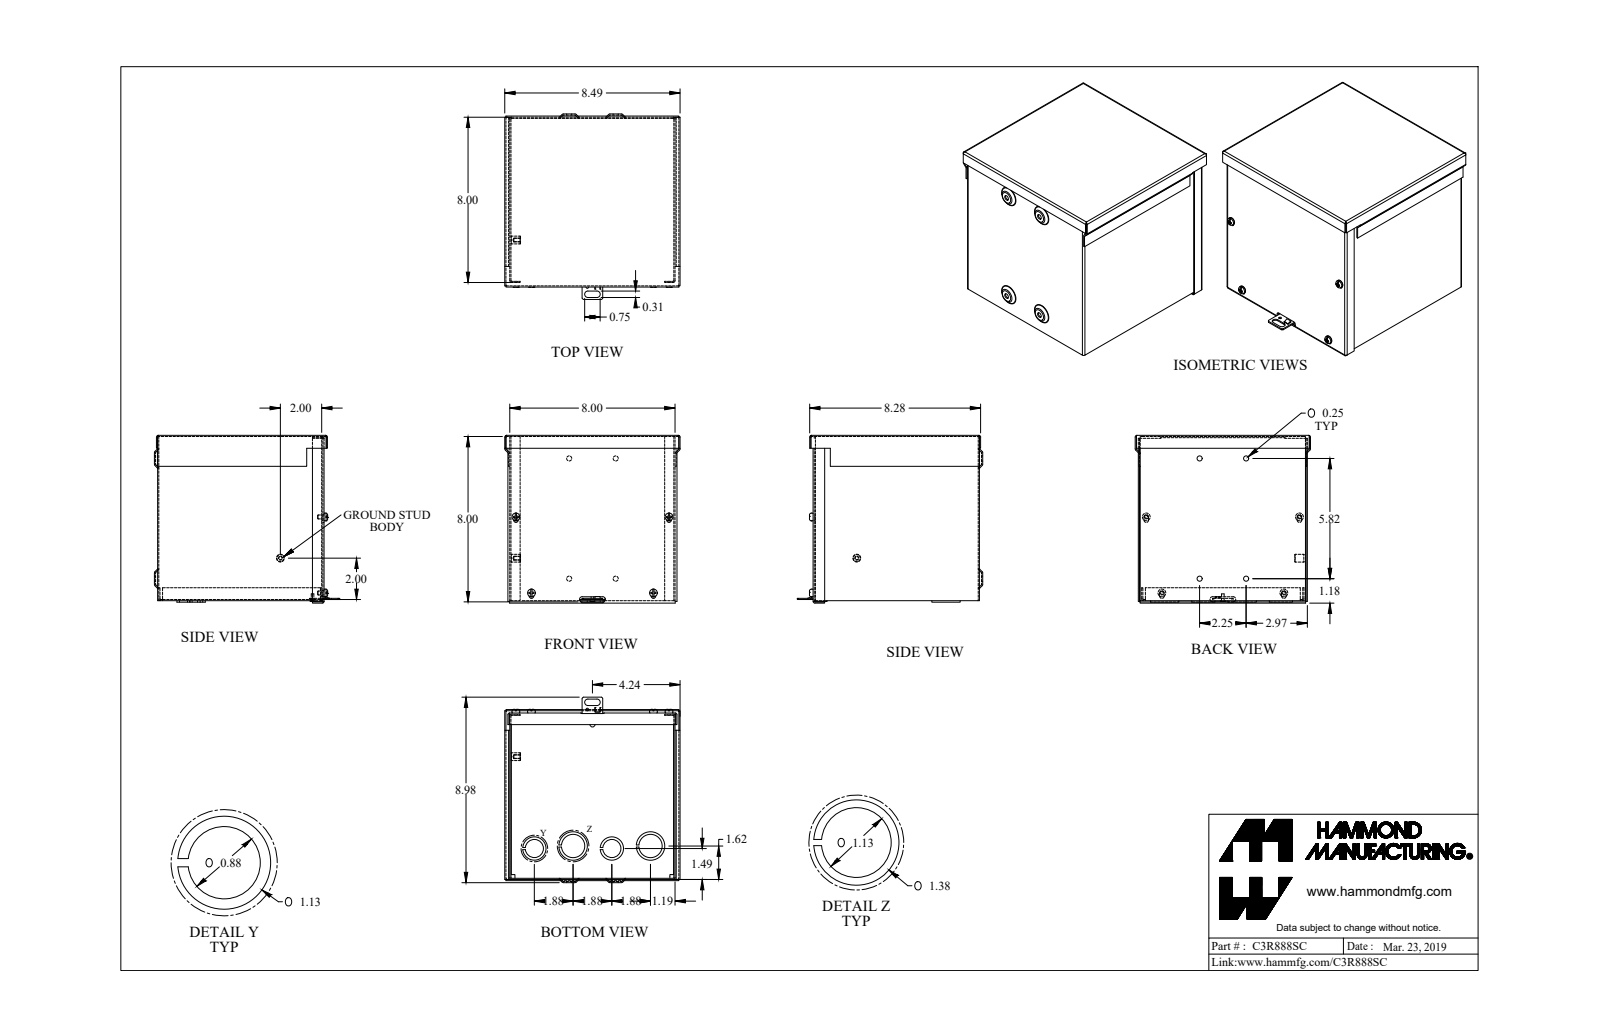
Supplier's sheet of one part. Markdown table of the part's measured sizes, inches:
| quantity | value |
| --- | --- |
| part name | C3R888SC_Default |
| STEP written by | SolidWorks 2019 (CONFIG_CONTROL_DESIGN) |
| units | inches |
| bodies | 11 solids, 424 faces (223 planar, 115 cylindrical, 86 other) |
| overall size | 8.977 × 8.489 × 8.12 |
| volume | 26.25 in³ |
| surface area | 929 in² |
| round holes (diameter × count) | 0.17 × 4, 0.25 × 4, 1.125 × 2, 0.125 × 1, 0.137 × 1, 0.156 × 1, 0.875 × 1, 0.875 × 1 |
| round bosses / shafts (diameter × count) | 0.375 × 4, 0.19 × 4, 1.375 × 2, 1.125 × 2, 0.375 × 1, 0.125 × 1 |
| partial cylindrical surfaces (radius × count) | 0.029 × 21, 0.086 × 21, 0.109 × 8, 0.125 × 8, 0.156 × 2 |
| main face-to-face distances | 0.057, 8, 7.943, 0.057, 7.886, 8.057, 7.886, 7.943, 0.114, 0.244 |
| hole center spacings | 3.89, 5.64, 1.88, 1.998, 2.25, 3.75, 3.752, 4.165 |
